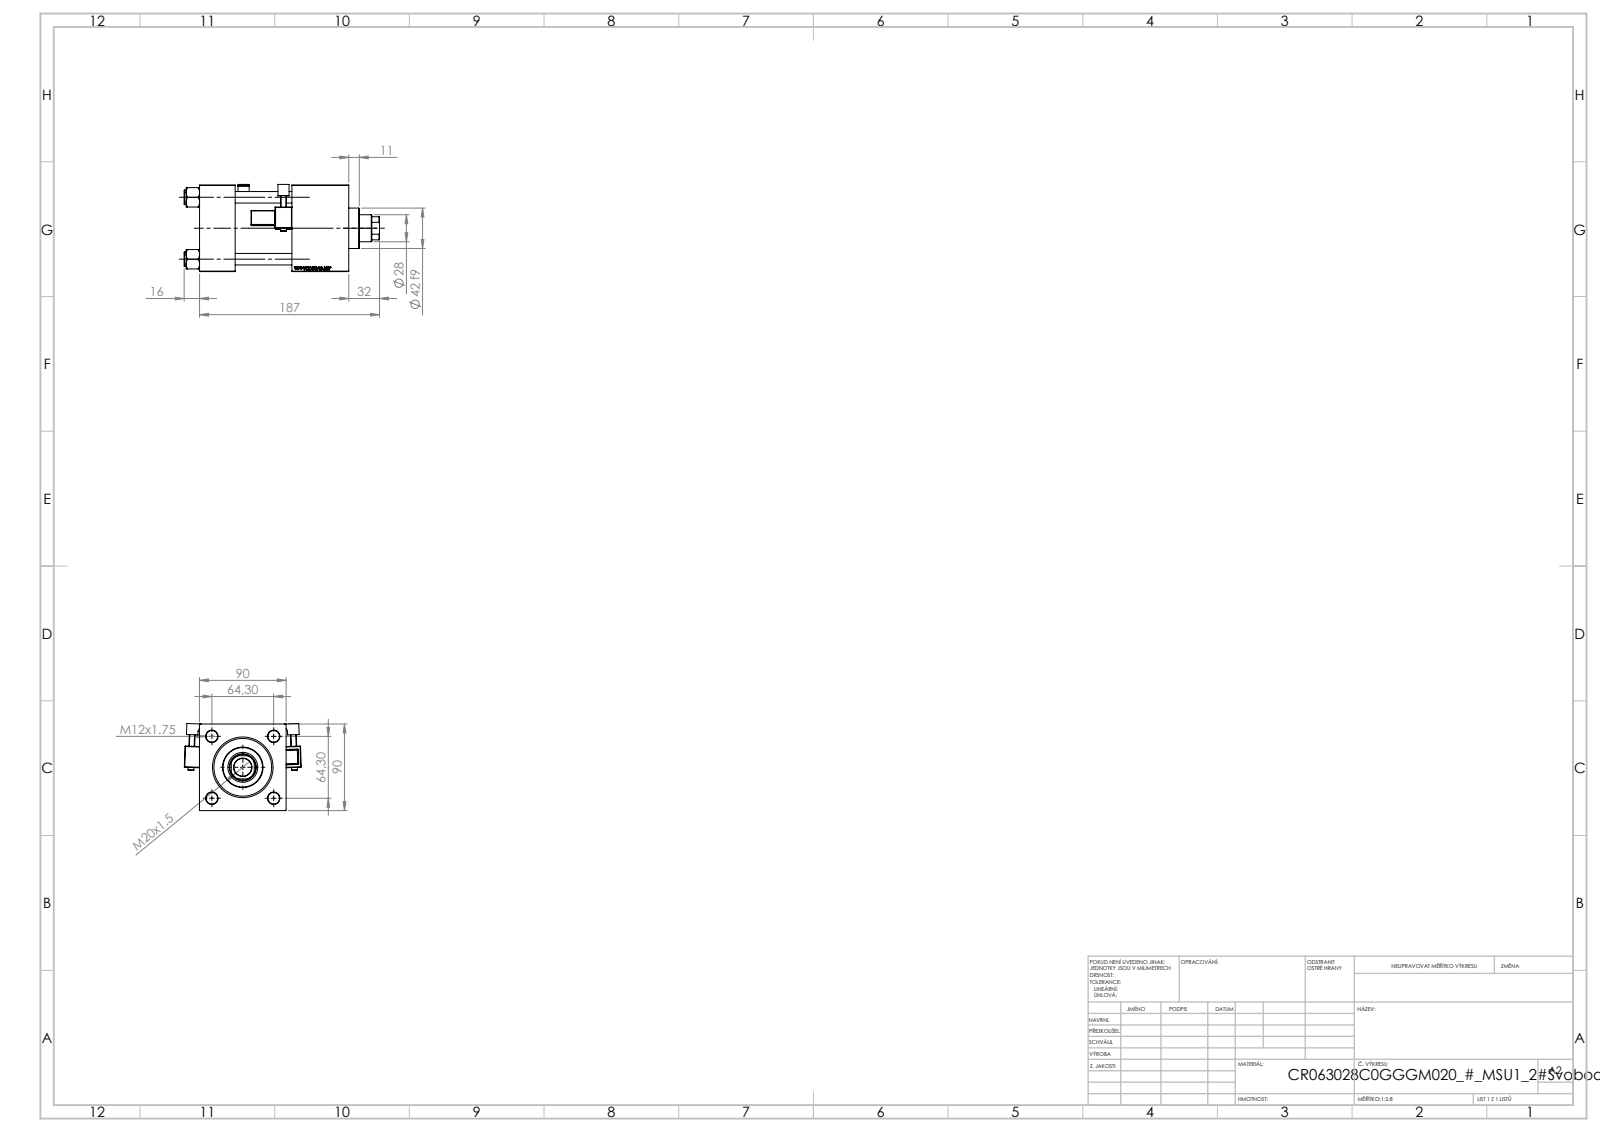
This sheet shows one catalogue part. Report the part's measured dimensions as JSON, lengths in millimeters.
{"part_name": "V215CR_VCP_C; V215CR_C_TYCINKA; V215CR_C_Body; V215CR_MSU (+2 more)", "step_written_by": "SolidWorks 2019 (CONFIG_CONTROL_DESIGN)", "units": "millimeters", "bodies": {"solids": 13, "faces": 1303, "planar": 584, "cylindrical": 147, "other": 572}, "overall_size": [203, 121.57, 90.53], "volume_mm3": 987909, "surface_area_mm2": 191403, "round_holes": [[12, 4], [7, 2], [20.96, 2], [30, 2], [18.5, 1], [28, 1], [31, 1], [50, 1], [60, 1], [63, 1]], "round_bosses_or_shafts": [[15, 4], [6, 2], [69, 1], [42, 1]], "partial_cylinders_radius": [[0.5, 48], [1, 2], [2.5, 2], [4, 2], [13.5, 1]], "face_to_face_distances": [90, 59, 37, 155, 118, 96, 126.3, 89.3, 30.3, 28.7], "hole_center_spacings": [45.47, 64.3, 90.93, 97.5]}
